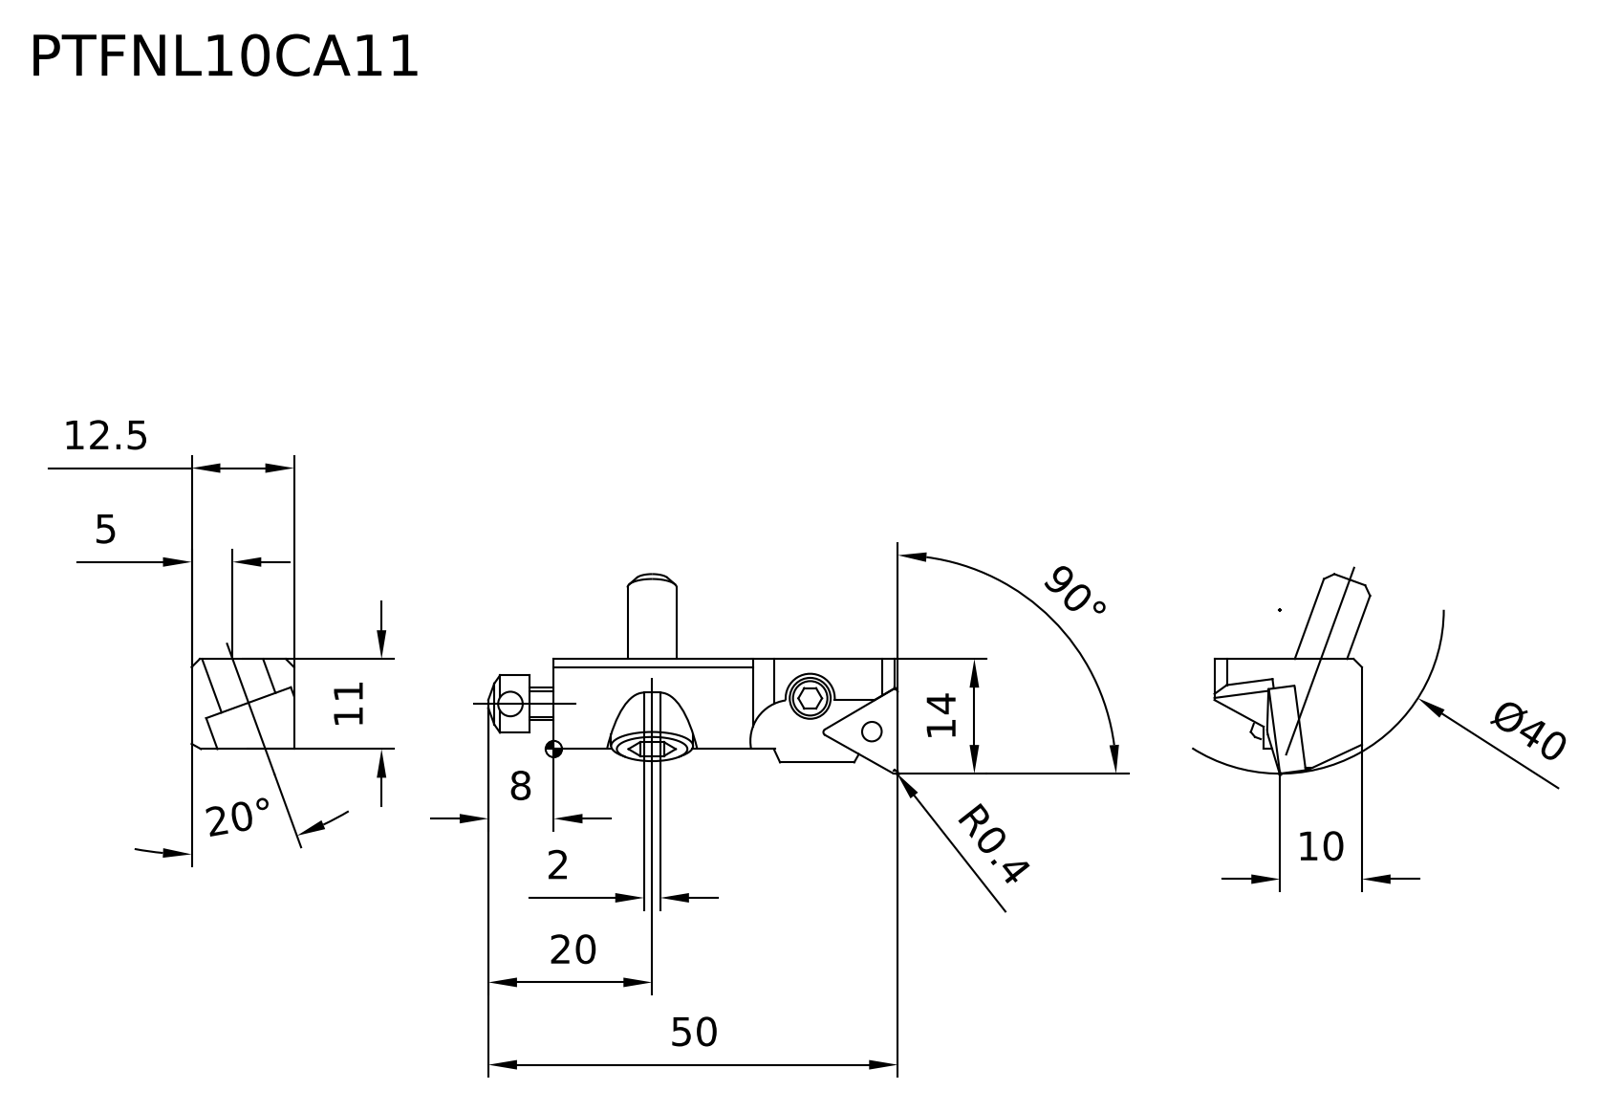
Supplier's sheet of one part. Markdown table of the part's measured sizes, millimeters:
| quantity | value |
| --- | --- |
| part name | PTFNL10CA11_ASM |
| STEP written by | SIEMENS PLM Software NX 10.0 (AUTOMOTIVE_DESIGN) |
| units | millimeters |
| bodies | 7 solids, 220 faces (110 planar, 68 cylindrical, 42 other) |
| overall size | 49.6 × 23.86 × 19 |
| volume | 5 761 mm³ |
| surface area | 4 419 mm² |
| round holes (diameter × count) | 1.8 × 2, 4.2 × 2, 2.05 × 1, 3.3 × 1 |
| round bosses / shafts (diameter × count) | 5 × 2, 10 × 1, 7 × 1, 6 × 1, 4 × 1, 3 × 1, 2.1 × 1, 1.7 × 1 |
| partial cylindrical surfaces (radius × count) | 0.2 × 12, 2 × 5, 0.5 × 4, 3.5 × 2, 5.5 × 2, 1.5 × 1, 1.7 × 1, 1.75 × 1 |
| main face-to-face distances | 11, 12.35, 41.6, 3, 18, 5.65, 12.45, 1.45, 6, 3.4 |
| hole center spacings | 43.69 |
